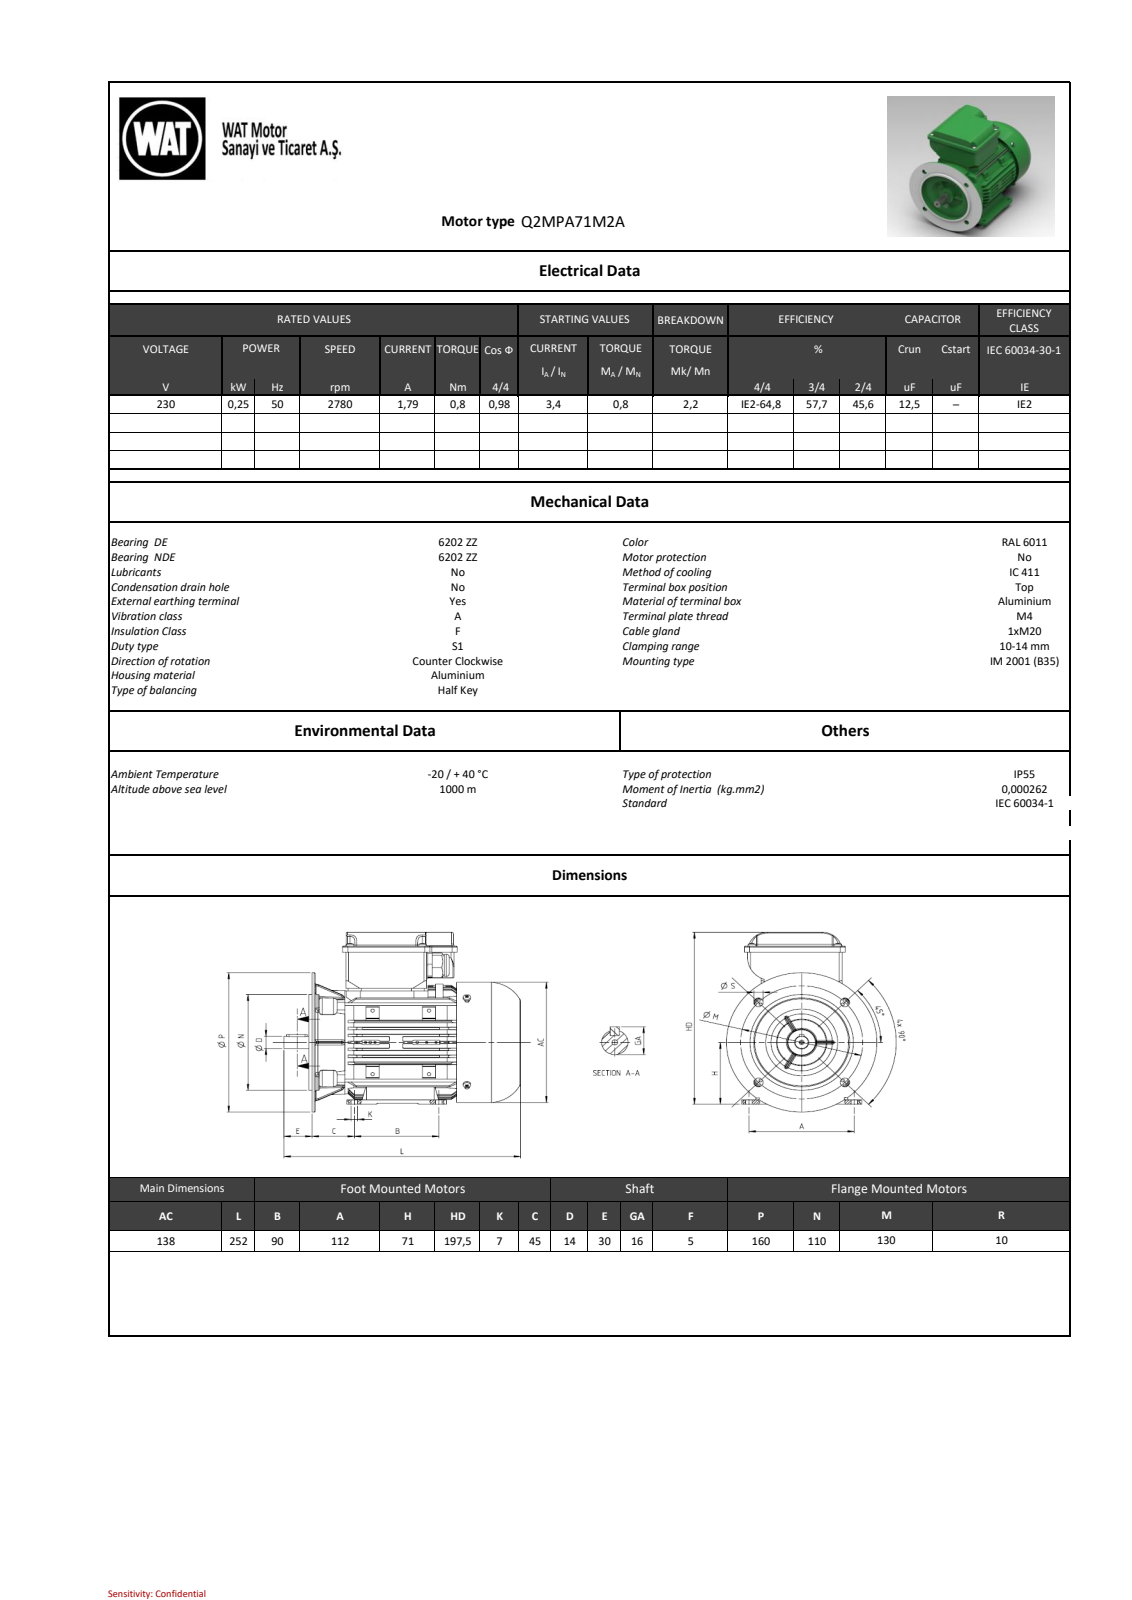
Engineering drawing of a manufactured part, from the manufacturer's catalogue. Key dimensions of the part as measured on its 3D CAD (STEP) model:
Part name (STEP PRODUCT): BY6424130xx_004-TKK_QM63-80; BY6434017xx_004-TK_QM63-80; BY6432282xx_005-MOTOR_KAPAGI_QS71FA_ISLEME_YENI; 641304741_AZ-KAMA PARALEL A 5x5x22 St50 DIN6885 (+8 more)
STEP written by: SIEMENS PLM Software NX2206.8101 (AUTOMOTIVE_DESIGN)
Units: millimetres
Bodies: 26 solids, 3055 faces (1315 planar, 833 cylindrical, 907 other)
Overall size (bounding box): 252 × 206.5 × 160
Volume: 807 723 mm³ · Surface area: 512 231 mm²
Round holes (diameter × count): ⌀3.3 ×13, ⌀3.65 ×8, ⌀4.5 ×8, ⌀2.5 ×6, ⌀4.65 ×4, ⌀4.8 ×4, ⌀5.2 ×4, ⌀7 ×4, ⌀10 ×4, ⌀3 ×3, ⌀3.7 ×3, ⌀4.6 ×2
Round bosses / shafts (diameter × count): ⌀8 ×8, ⌀4 ×8, ⌀3 ×8, ⌀160 ×1, ⌀138 ×1, ⌀136 ×1, ⌀110 ×1, ⌀26 ×1
Partial cylindrical surfaces — rounded edges, fillets, slot ends (radius × count): R1 ×157, R2 ×72, R0.5 ×38, R1.2 ×36, R10 ×24, R0.75 ×18, R2.5 ×14, R4 ×14
Main face-to-face distances: 3, 5, 4, 185.5, 1, 67.5, 177.2, 2, 146.5, 189.5
Hole centre spacings: 89.74, 55, 36.59, 65, 60, 3.13, 28.5, 37.26
